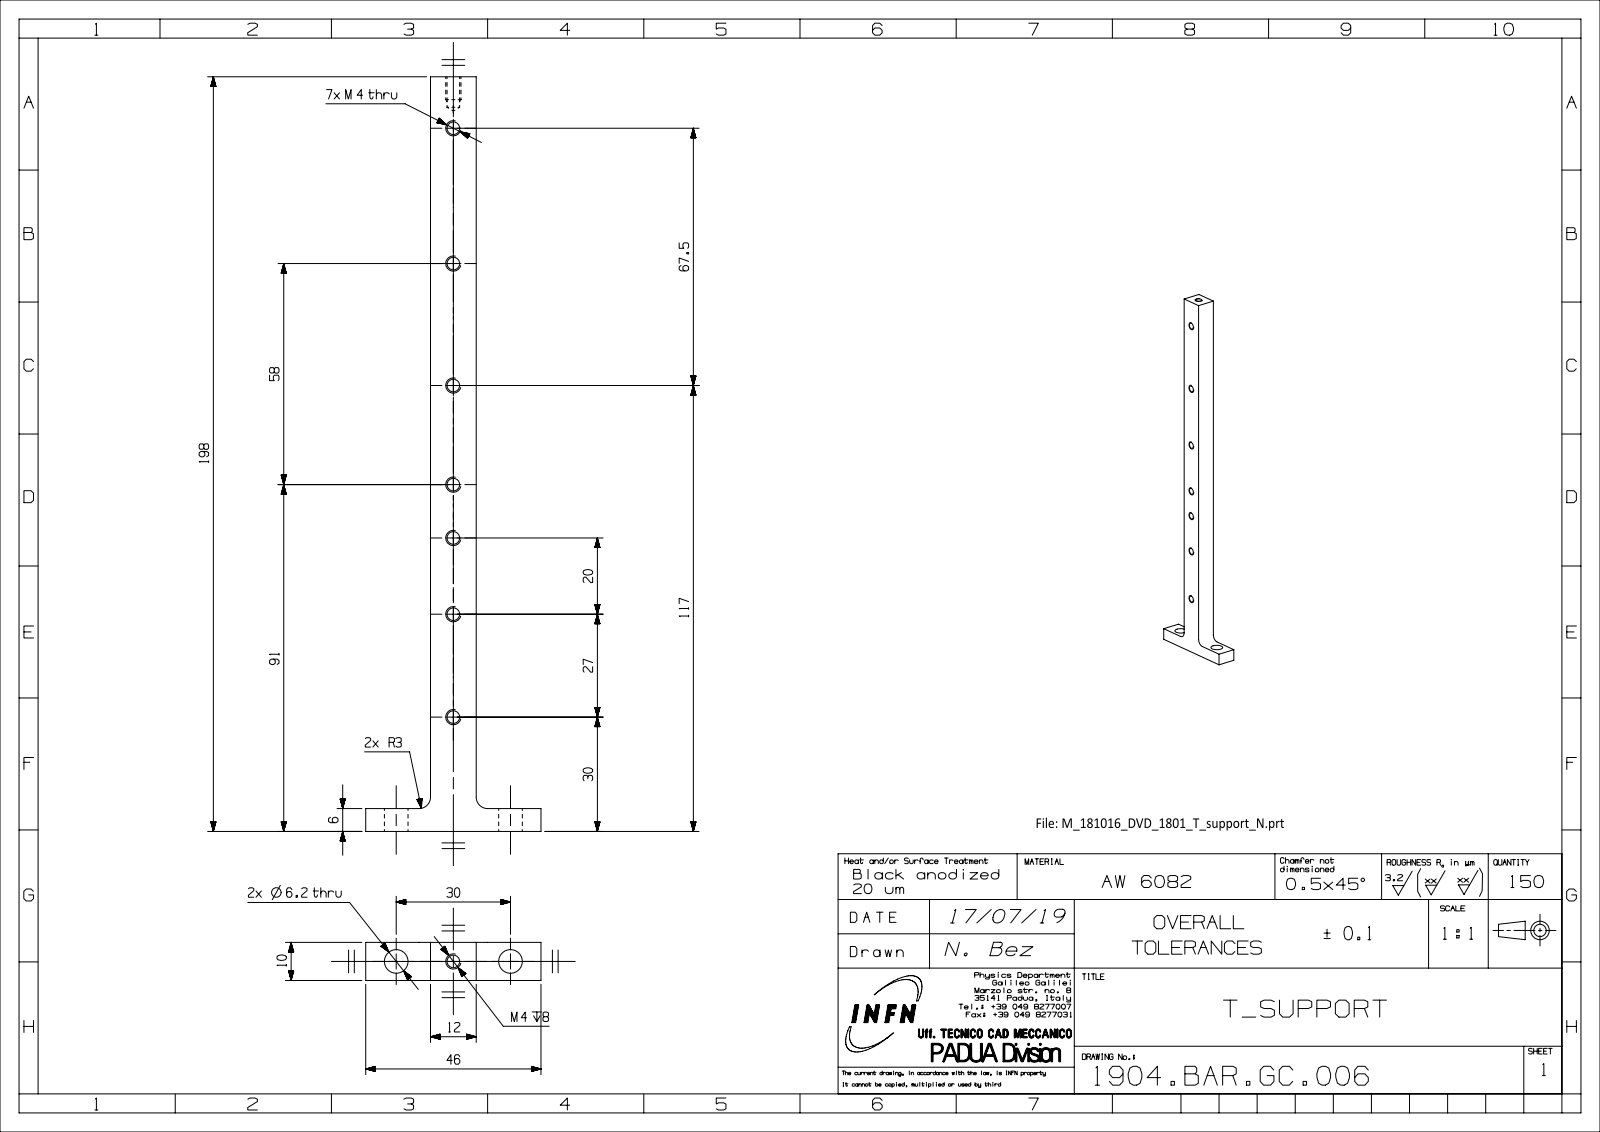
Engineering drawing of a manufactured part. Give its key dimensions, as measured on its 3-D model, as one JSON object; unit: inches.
{"part_name": "bmas477C8C18u67q", "step_written_by": "SIEMENS PLM Software NX 12.0 (AUTOMOTIVE_DESIGN)", "units": "inches", "bodies": {"solids": 1, "faces": 23, "planar": 10, "cylindrical": 12, "other": 1}, "overall_size": [7.795, 1.811, 0.394], "volume_in3": 1.514, "surface_area_in2": 16.78, "round_holes": [[0.13, 8], [0.244, 2]], "partial_cylinders_radius": [[0.118, 2]], "face_to_face_distances": [0.394, 0.472, 0.236, 0.669, 1.142, 7.795, 7.559, 1.811], "hole_center_spacings": [0.591, 0.551, 0.787, 1.024, 1.063, 1.181, 1.26, 1.339]}
